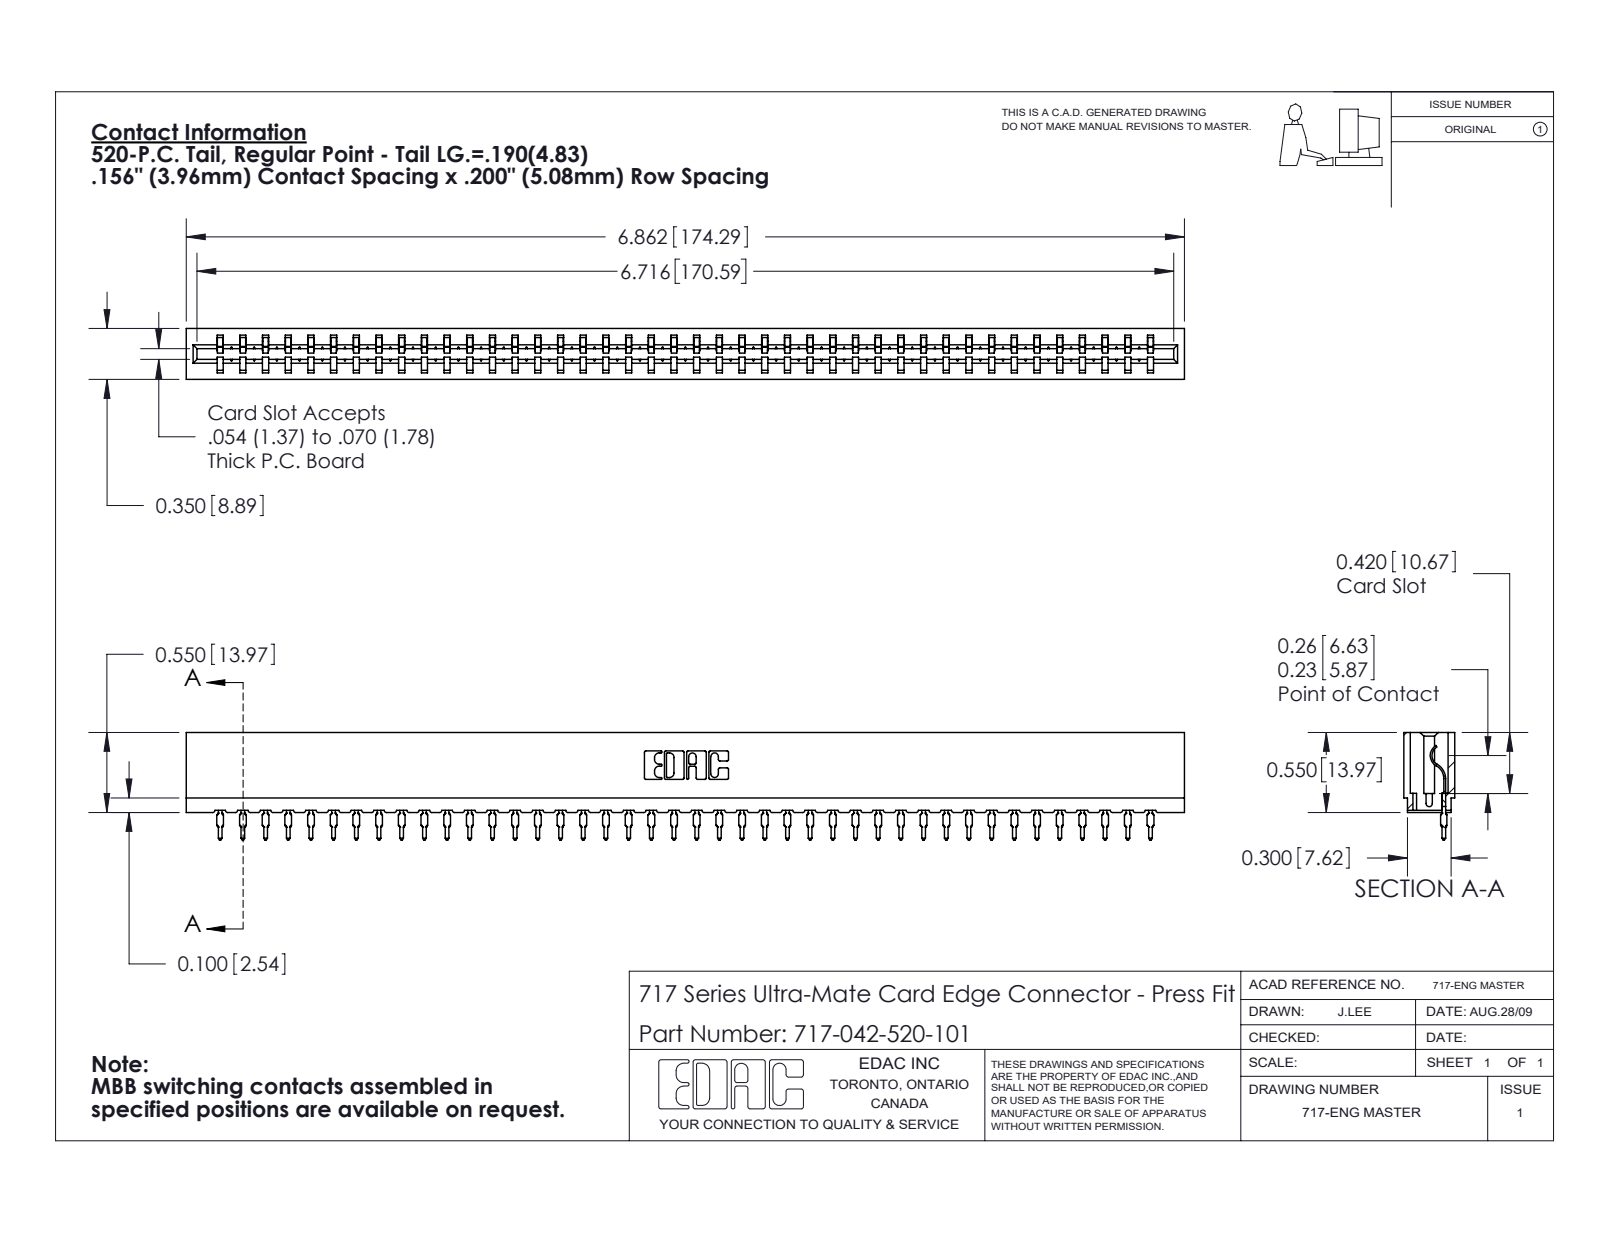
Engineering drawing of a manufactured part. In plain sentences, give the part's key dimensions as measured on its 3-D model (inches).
The part is named "717-042-520-101; 717 Part_Insulator Option - 06; 745-292-001_520". Its 3-D file was written by "SolidWorks 2020 (CONFIG_CONTROL_DESIGN)". It is 43 solids with 4840 faces: 2910 planar, 838 cylindrical and 1092 other. Overall it measures 6.862 by 0.739 by 0.35 inches. Its volume is 0.894 cubic inches and its surface area 31.45 square inches. Partial cylindrical surfaces (rounded edges, fillets, slot ends): 84 of radius 0.015, 84 of radius 0.021, 22 of radius 0.01, 6 of radius 0.007, 6 of radius 0.031, 4 of radius 0.005, 4 of radius 0.011, 3 of radius 0.026. The main face-to-face distances are 0.212, 0.138, 0.35, 0.074, 0.045, 0.305, 0.093, 0.167, 0.025, 0.063.
